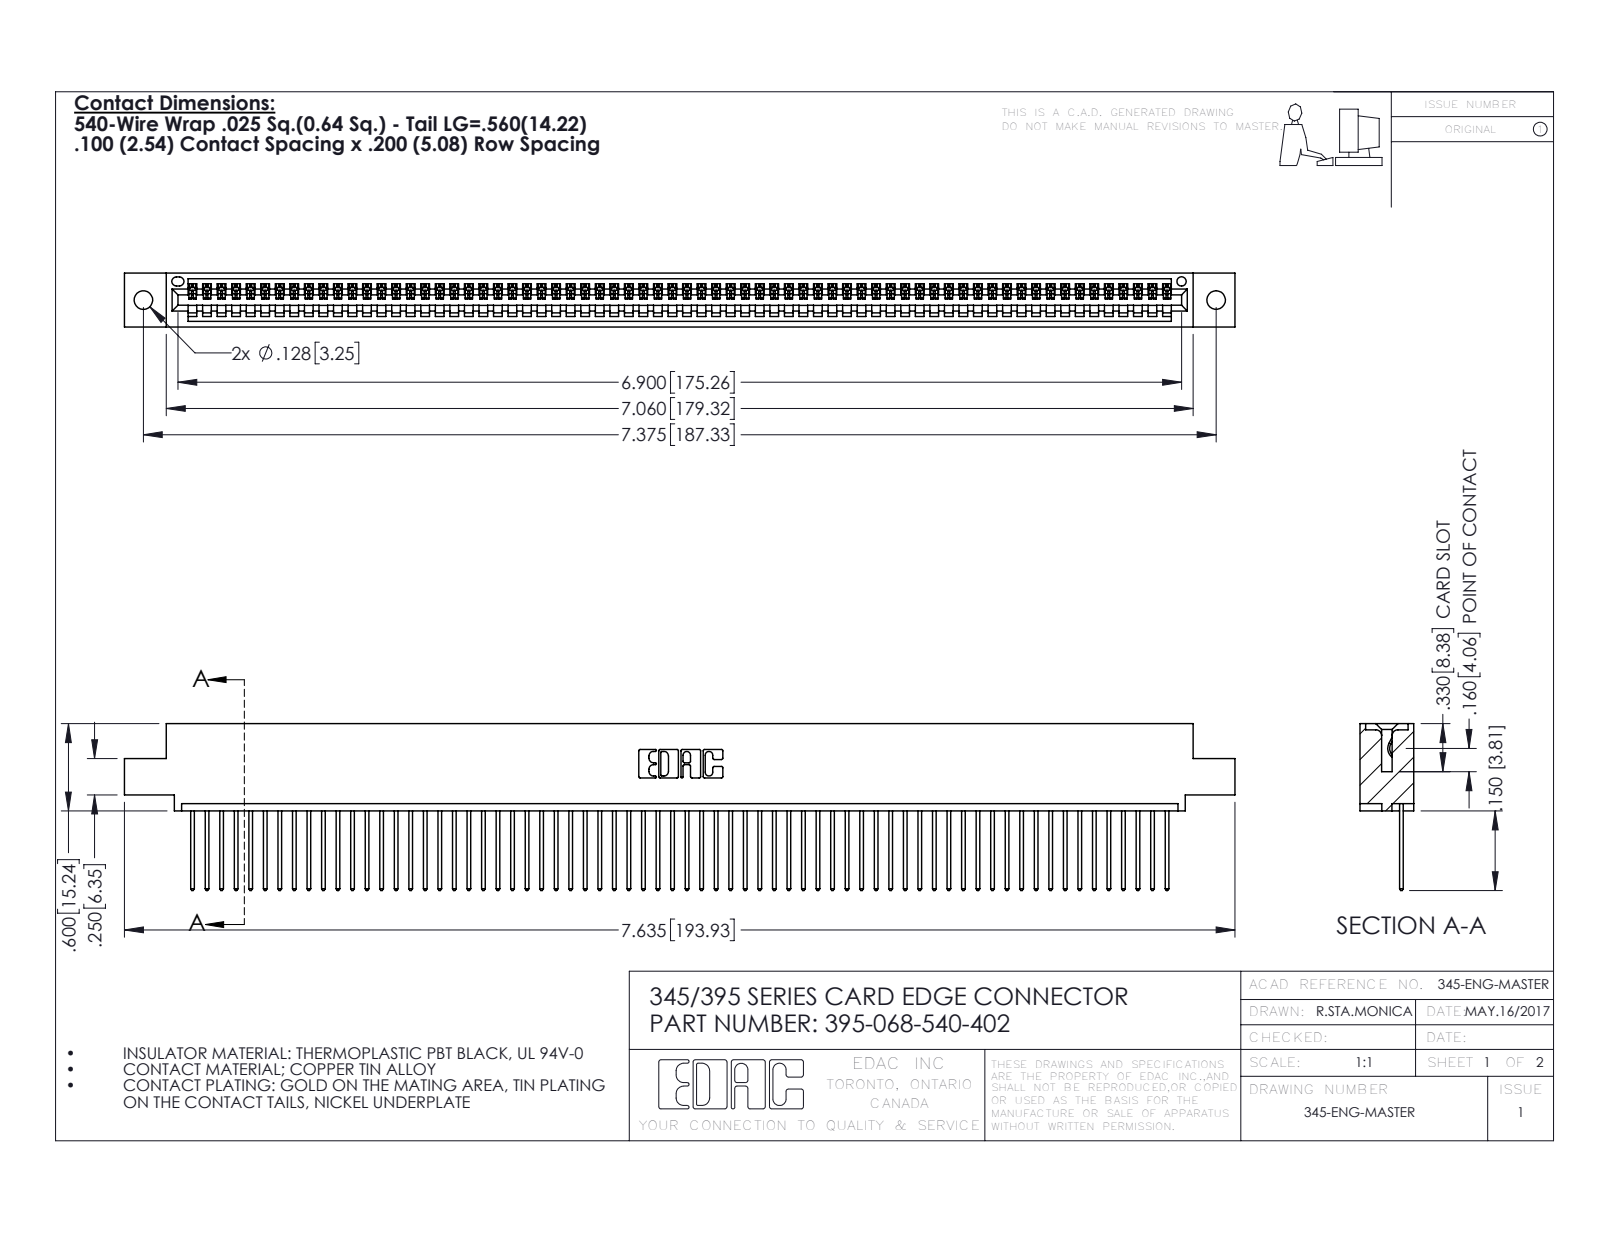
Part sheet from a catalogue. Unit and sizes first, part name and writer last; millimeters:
Units: millimetres
Overall size (bounding box): 193.9 × 29.1 × 9.4
Round holes (diameter × count): ⌀3.3 ×2, ⌀1.6 ×1
Partial cylindrical surfaces — rounded edges, fillets, slot ends (radius × count): R0.2 ×136, R0.3 ×136, R0.3 ×22, R0.2 ×6, R0.8 ×6, R0.7 ×3, R0.8 ×2, R1 ×2
Main face-to-face distances: 1.8, 7.6, 9.4, 2.5, 6.9, 0.6, 5.1, 5.7, 3.8, 1.8
Hole centre spacings: 6.9, 181.3, 187.3
Volume: 18 620 mm³ · Surface area: 25 560 mm²
Bodies: 69 solids, 4074 faces (2804 planar, 1270 cylindrical, 0 other)
Part name (STEP PRODUCT): 395-068-540-402; 345-292-001_345-293-140; 345 Part_0.110 Offset - 0.128 Dia
STEP written by: SolidWorks 2016 (CONFIG_CONTROL_DESIGN)
